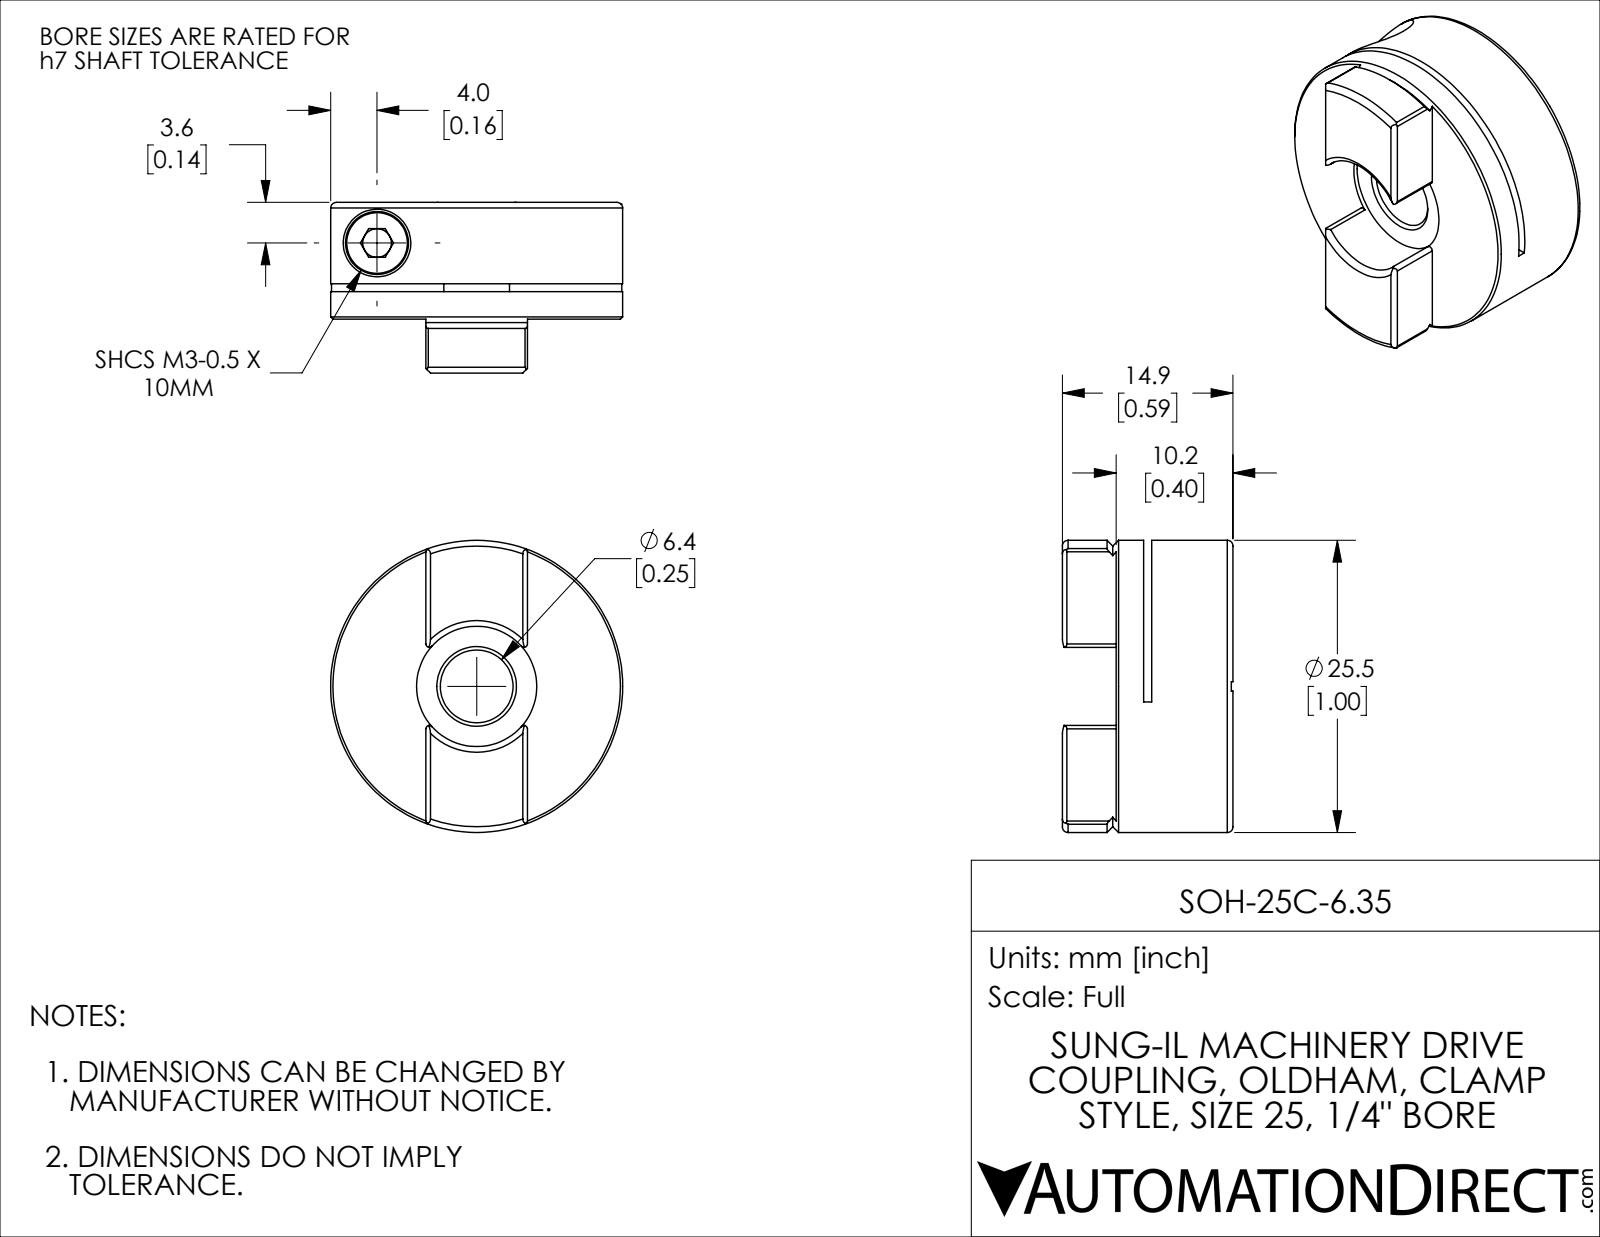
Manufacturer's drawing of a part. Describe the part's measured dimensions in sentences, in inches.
The part is named "SOH-25C-6.35". Its 3-D file was written by "SolidWorks 2021 (CONFIG_CONTROL_DESIGN)". It is 2 solids with 99 faces: 40 planar, 33 cylindrical and 26 other. Overall it measures 1.004 by 1.004 by 0.587 inches. Its volume is 0.313 cubic inches and its surface area 5.169 square inches. Round holes: 1 of diameter 0.098, 1 of diameter 0.13, 1 of diameter 0.232, 1 of diameter 0.25, 1 of diameter 0.413. Round bosses or shafts: 1 of diameter 1.004, 1 of diameter 0.217, 1 of diameter 0.118. Partial cylindrical surfaces (rounded edges, fillets, slot ends): 8 of radius 0.012, 1 of radius 0.886. The main face-to-face distances are 0.307, 0.28, 0.402, 0.094, 0.028, 0.122, 0.587, 0.185, 0.031, 0.349.
